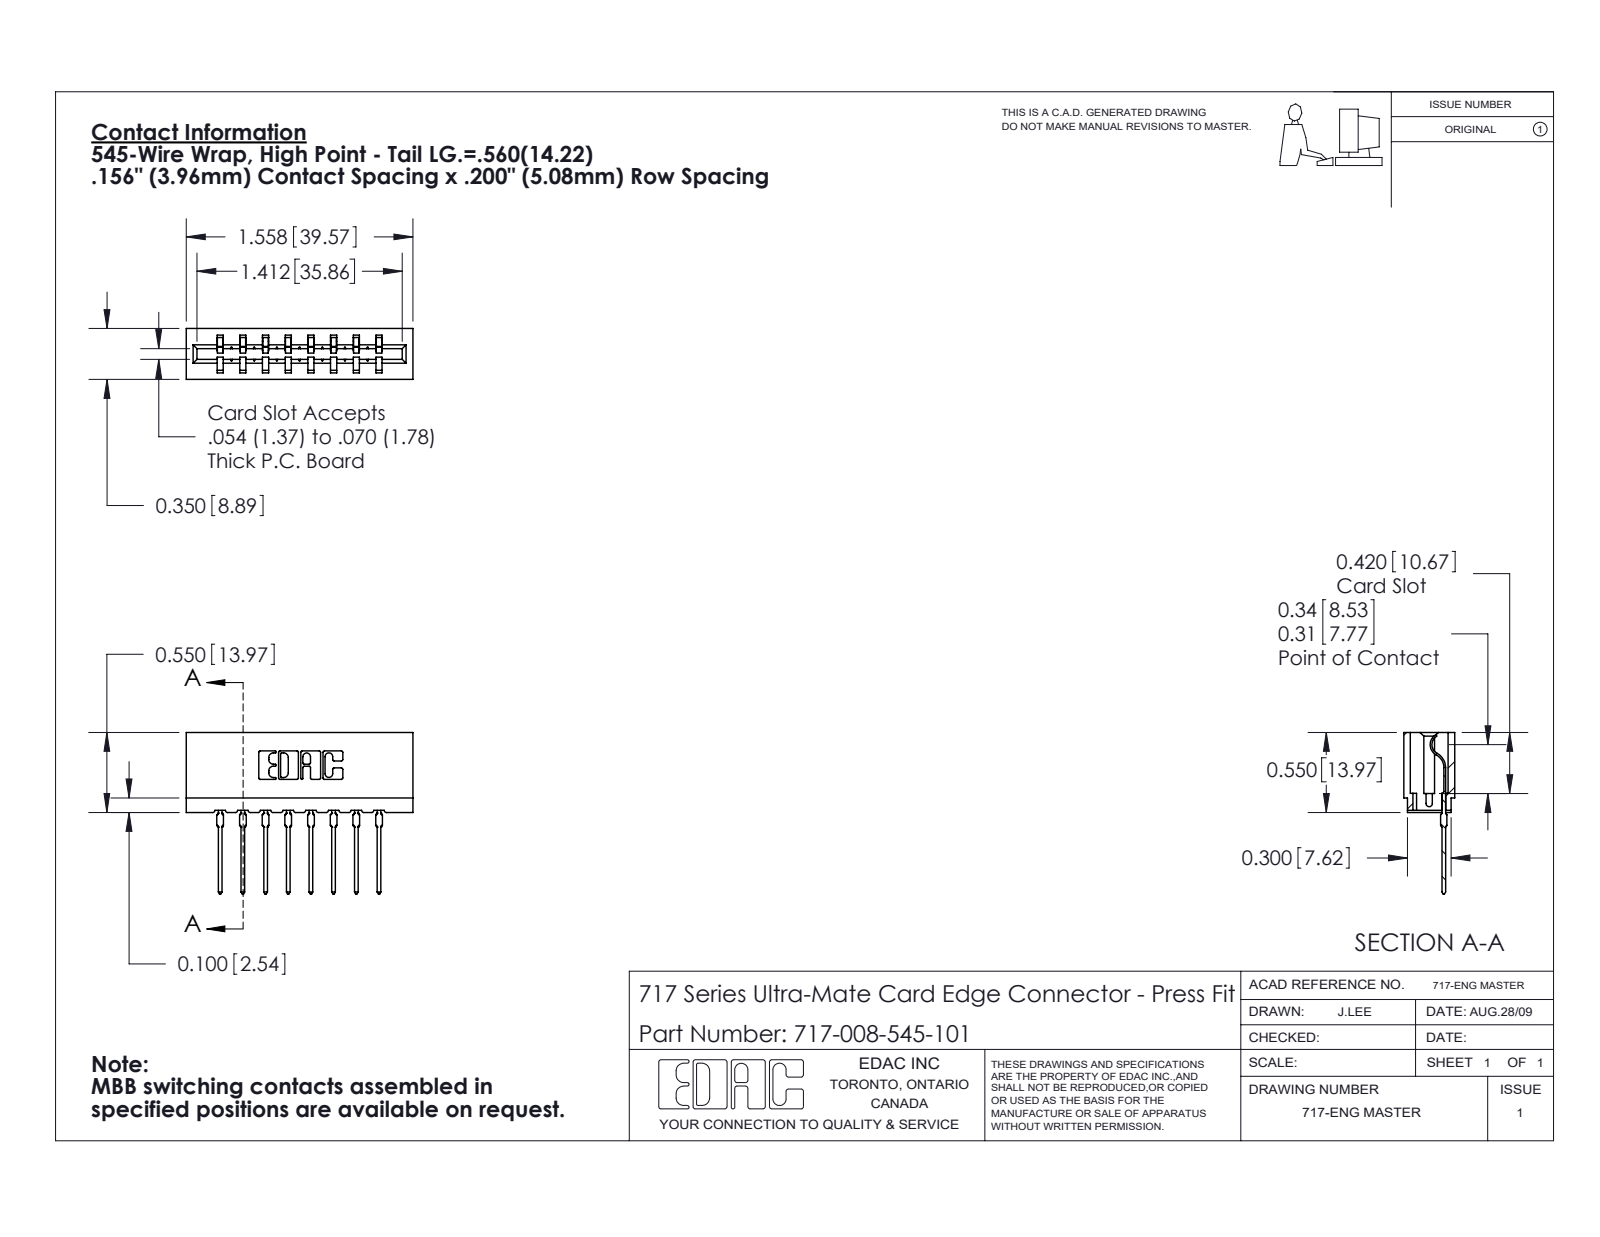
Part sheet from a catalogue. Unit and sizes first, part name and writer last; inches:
Units: inches
Overall size (bounding box): 1.558 × 1.109 × 0.35
Partial cylindrical surfaces — rounded edges, fillets, slot ends (radius × count): R0.01 ×22, R0.015 ×16, R0.021 ×16, R0.007 ×6, R0.031 ×6, R0.005 ×4, R0.011 ×4, R0.026 ×3
Main face-to-face distances: 0.212, 0.156, 0.138, 0.624, 0.468, 0.198, 0.312, 0.35, 0.042, 0.27
Volume: 0.215 in³ · Surface area: 7.282 in²
Bodies: 9 solids, 998 faces (598 planar, 192 cylindrical, 208 other)
Part name (STEP PRODUCT): 717-008-545-101; 745-292-001_545; 717 Part_Insulator Option - 06
STEP written by: SolidWorks 2020 (CONFIG_CONTROL_DESIGN)
